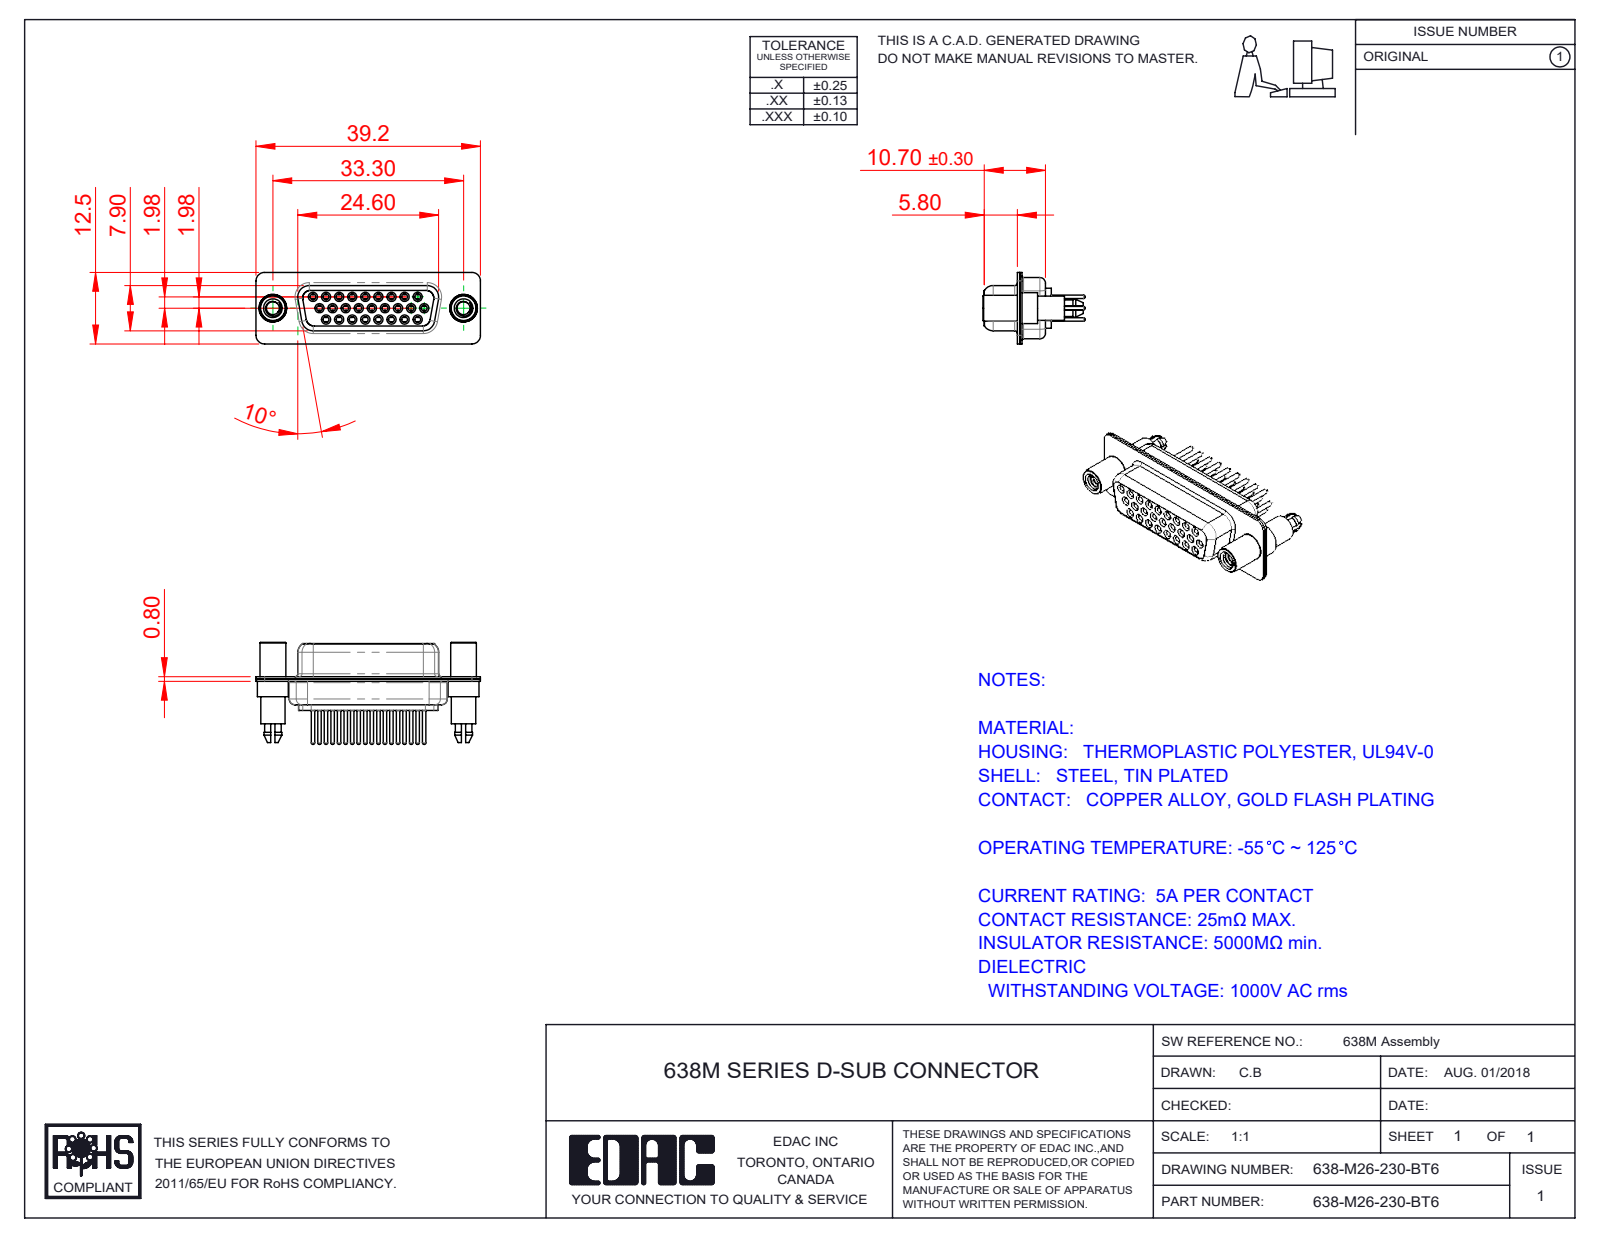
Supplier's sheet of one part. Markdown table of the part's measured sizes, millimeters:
| quantity | value |
| --- | --- |
| part name | 638M Contact Row 2_30; 638M 4-40 Threaded Standoff and Boardlock; 638M Contact Row 1_30; 638-M26-230-BT6 (+4 more) |
| STEP written by | SolidWorks 2020 (CONFIG_CONTROL_DESIGN) |
| units | millimeters |
| bodies | 31 solids, 1793 faces (495 planar, 667 cylindrical, 631 other) |
| overall size | 39.2 × 17.8 × 12.5 |
| volume | 2 690 mm³ |
| surface area | 8 346 mm² |
| round holes (diameter × count) | 1 × 26, 1.1 × 26, 1.7 × 26, 1.8 × 26, 2 × 26, 2.26 × 2, 4 × 2, 4.8 × 2 |
| round bosses / shafts (diameter × count) | 2.2 × 26, 1.6 × 26, 1.5 × 26, 0.6 × 26, 5.4 × 2, 4.9 × 2, 4.5 × 2, 4.25 × 2 |
| partial cylindrical surfaces (radius × count) | 1.5 × 18, 2 × 12, 1.6 × 10, 1.35 × 8, 0.25 × 4, 0.5 × 4, 0.6 × 4, 0.65 × 4 |
| main face-to-face distances | 0.4, 1.4, 0.45, 8.45, 8.9, 1, 1.8, 6.2, 7.05, 9.3 |
| hole center spacings | 3.96, 2.28, 4.57, 6.05, 2.29, 8.24, 6.86, 6.04 |
